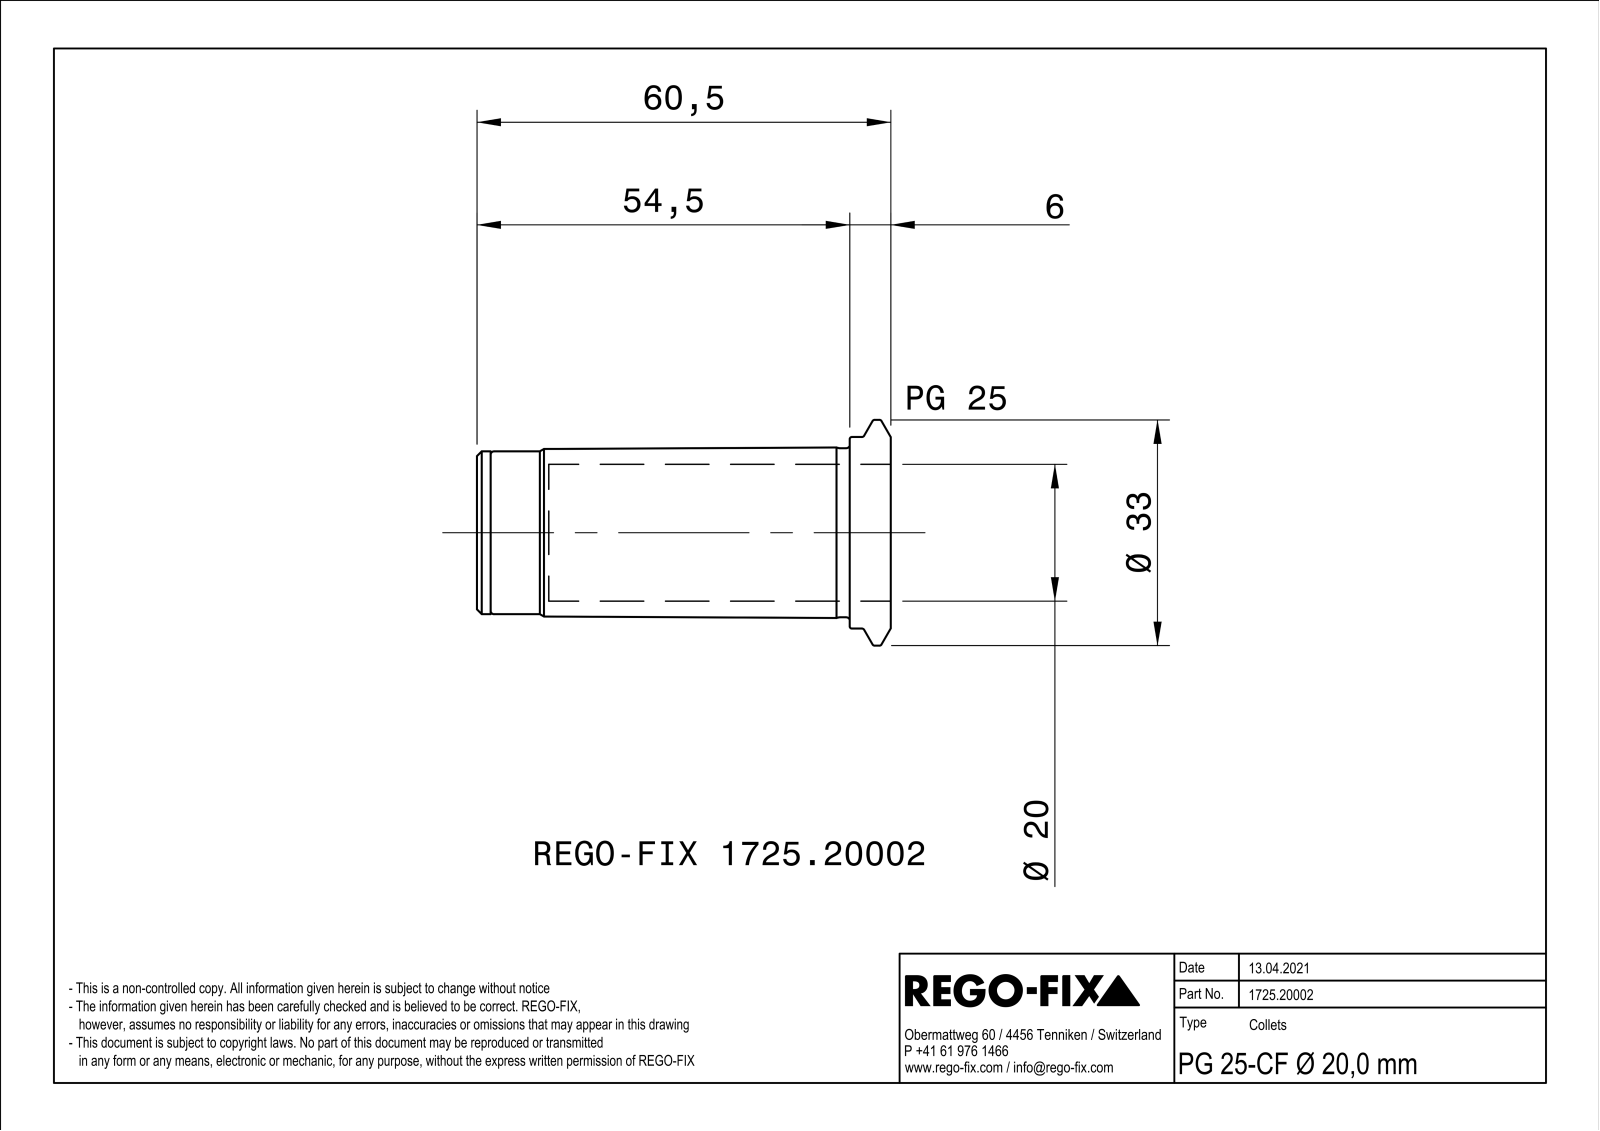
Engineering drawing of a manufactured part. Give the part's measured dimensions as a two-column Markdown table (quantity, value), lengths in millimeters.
| quantity | value |
| --- | --- |
| part name | NOCUT |
| STEP written by | SIEMENS PLM Software Solid Edge ST10 (AUTOMOTIVE_DESIGN) |
| units | millimeters |
| bodies | 1 solid, 96 faces (23 planar, 35 cylindrical, 38 other) |
| overall size | 60.5 × 33 × 32.99 |
| volume | 12 644 mm³ |
| surface area | 11 162 mm² |
| round holes (diameter × count) | 2.5 × 3, 5.2 × 1, 6.92 × 1, 8.2 × 1, 20 × 1, 20.92 × 1, 22.2 × 1 |
| round bosses / shafts (diameter × count) | 33 × 1, 28 × 1, 24.7 × 1, 23.8 × 1, 20.4 × 1, 12 × 1 |
| partial cylindrical surfaces (radius × count) | 0.75 × 3 |
| main face-to-face distances | 1, 60.5, 52.6, 7.9, 58.5, 5.9, 2, 50, 2.6, 8.5 |
| hole center spacings | 7.75, 13.43, 13.42 |
